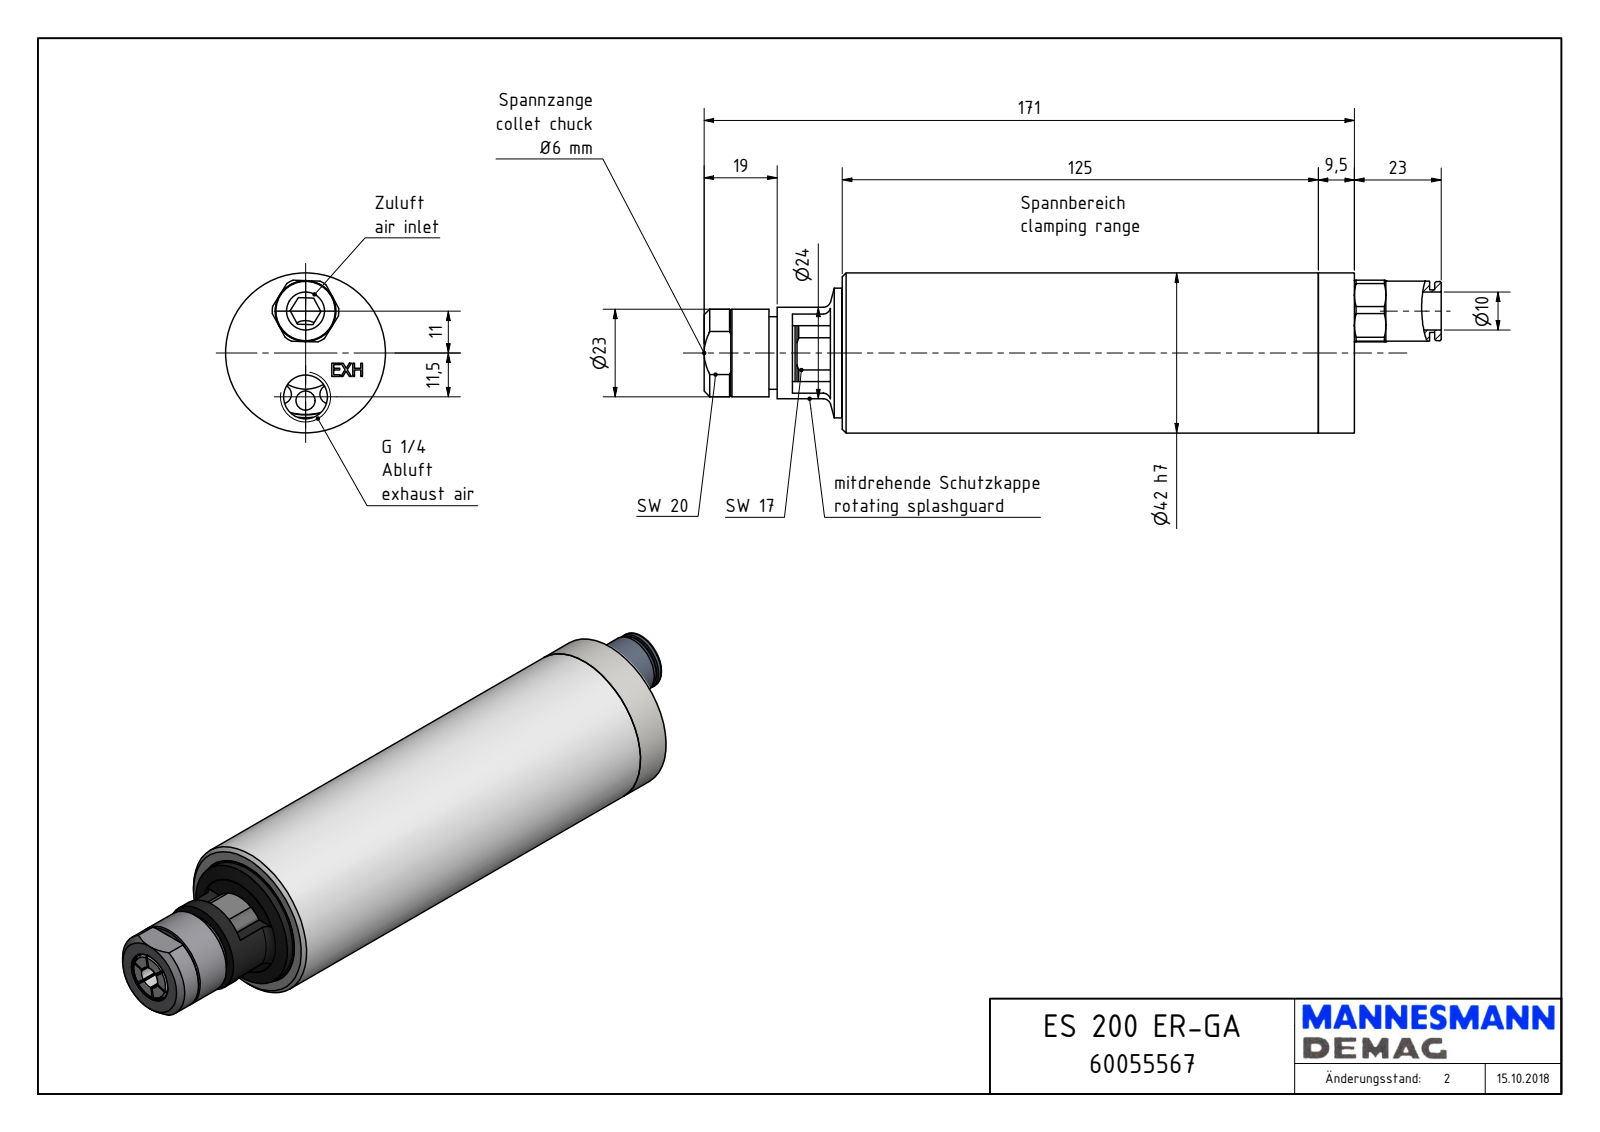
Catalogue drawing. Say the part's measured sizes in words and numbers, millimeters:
The part is named "ES 200 ER-GA_60055567". Its 3-D file was written by "Autodesk Inventor 2021 (AUTOMOTIVE_DESIGN)". It is 1 solid with 222 faces: 123 planar, 48 cylindrical and 51 other. Overall it measures 193.54 by 42 by 42 millimeters. Its volume is 201 332 cubic millimeters and its surface area 29 911 square millimeters. Round holes: 2 of diameter 11.45, 1 of diameter 6, 1 of diameter 10, 1 of diameter 13.2, 1 of diameter 13.95, 1 of diameter 34.92. Round bosses or shafts: 1 of diameter 42, 1 of diameter 34, 1 of diameter 29.1, 1 of diameter 24, 1 of diameter 23, 1 of diameter 19, 1 of diameter 15.75, 1 of diameter 15.5. Partial cylindrical surfaces (rounded edges, fillets, slot ends): 6 of radius 18.09, 6 of radius 33.72, 1 of radius 7, 1 of radius 8.75. The main face-to-face distances are 0.5, 19.17, 134.5, 17, 134.42, 3, 36.29, 36.37, 170.79, 161.65. The hole center spacings are 11, 11.5, 22.5.
